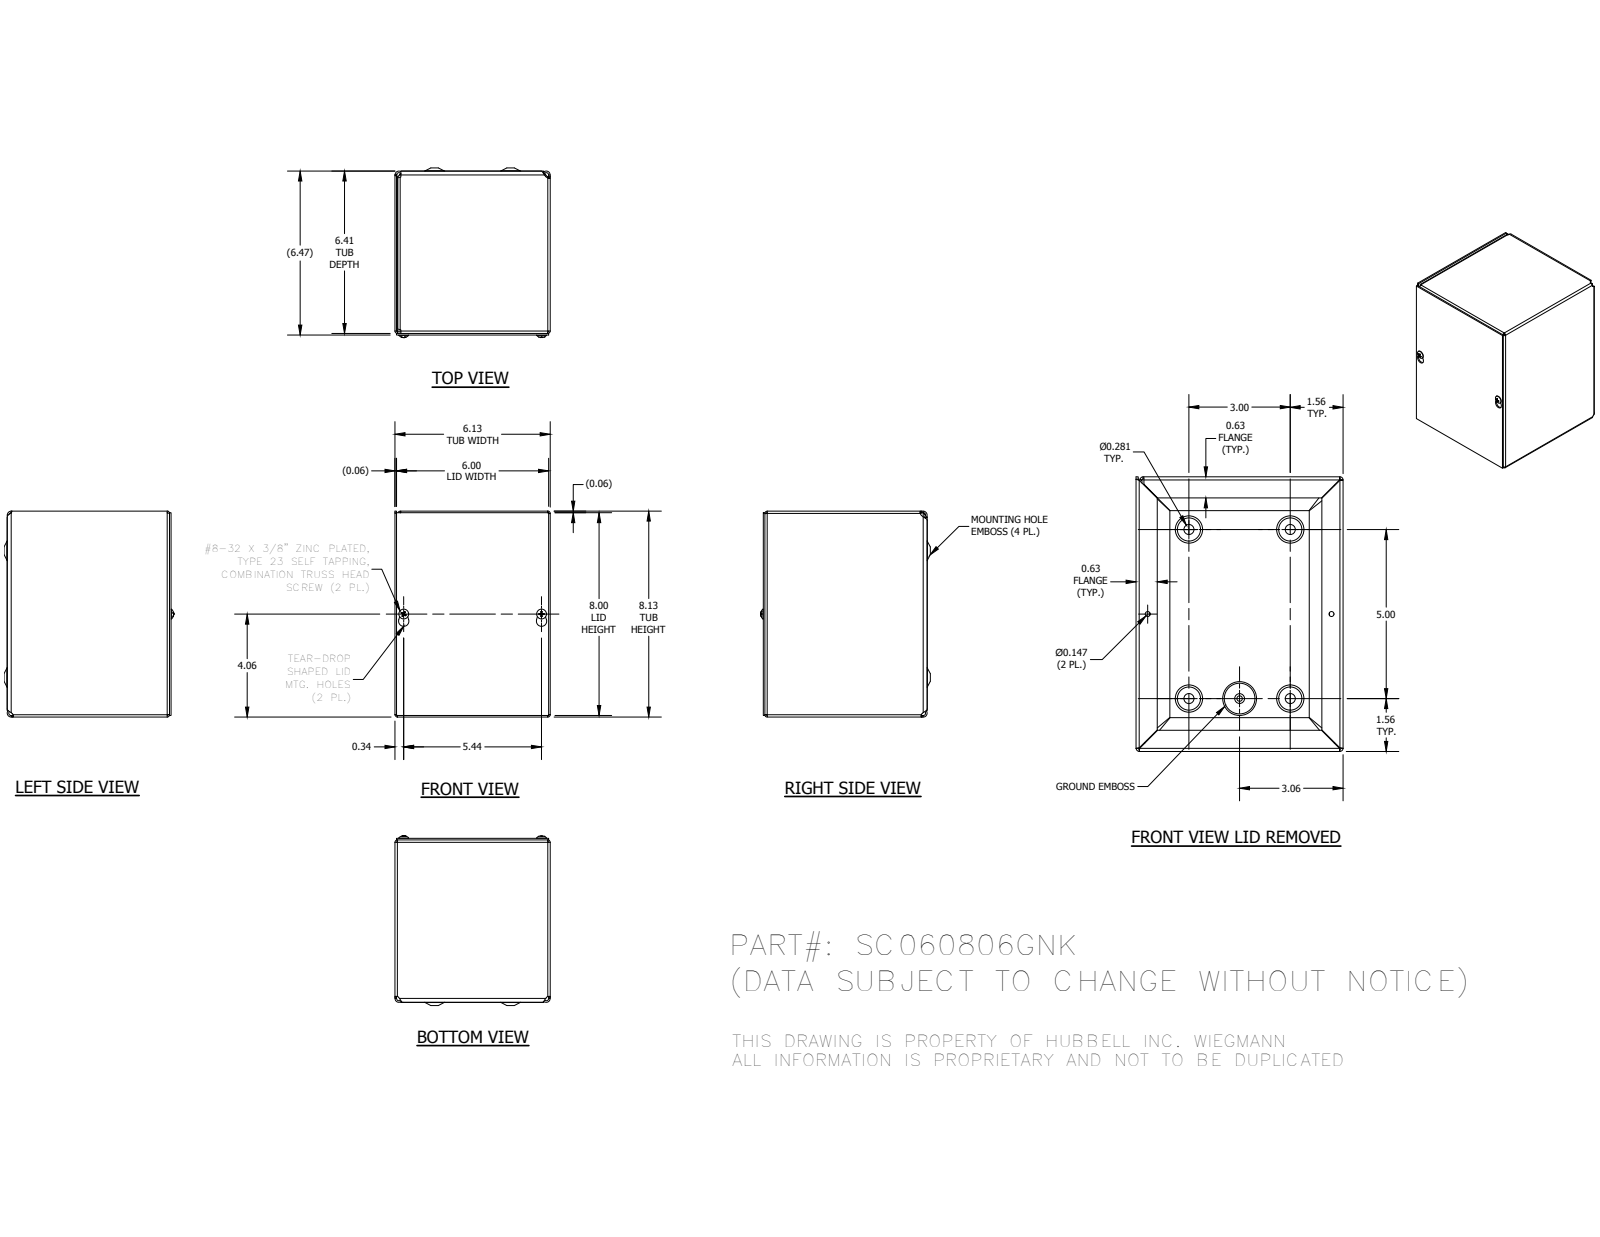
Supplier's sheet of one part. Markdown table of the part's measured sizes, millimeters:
| quantity | value |
| --- | --- |
| part name | SC0608GNKBKP; SC060806GNKWRA; SC0608GNKLID; 34056 (+1 more) |
| STEP written by | Autodesk Inventor 2014 (AUTOMOTIVE_DESIGN) |
| units | millimeters |
| bodies | 5 solids, 294 faces (109 planar, 63 cylindrical, 122 other) |
| overall size | 206.38 × 170 × 155.57 |
| volume | 314 400 mm³ |
| surface area | 404 865 mm² |
| round holes (diameter × count) | 7.62 × 4, 3.73 × 2, 4.19 × 1 |
| round bosses / shafts (diameter × count) | 9.75 × 2, 4.17 × 2, 5.8 × 1 |
| partial cylindrical surfaces (radius × count) | 0.79 × 8, 2.37 × 8, 1.4 × 4, 1.57 × 4, 2.38 × 4, 2.97 × 4, 3.15 × 4, 3.96 × 4 |
| main face-to-face distances | 1.57, 154, 204.8, 161.12, 155.57, 152.43, 162.69, 1.59, 162.71, 164.28 |
| hole center spacings | 38.1, 70.66, 76.2, 93.8, 127, 132.59, 148.11, 70.62 |
